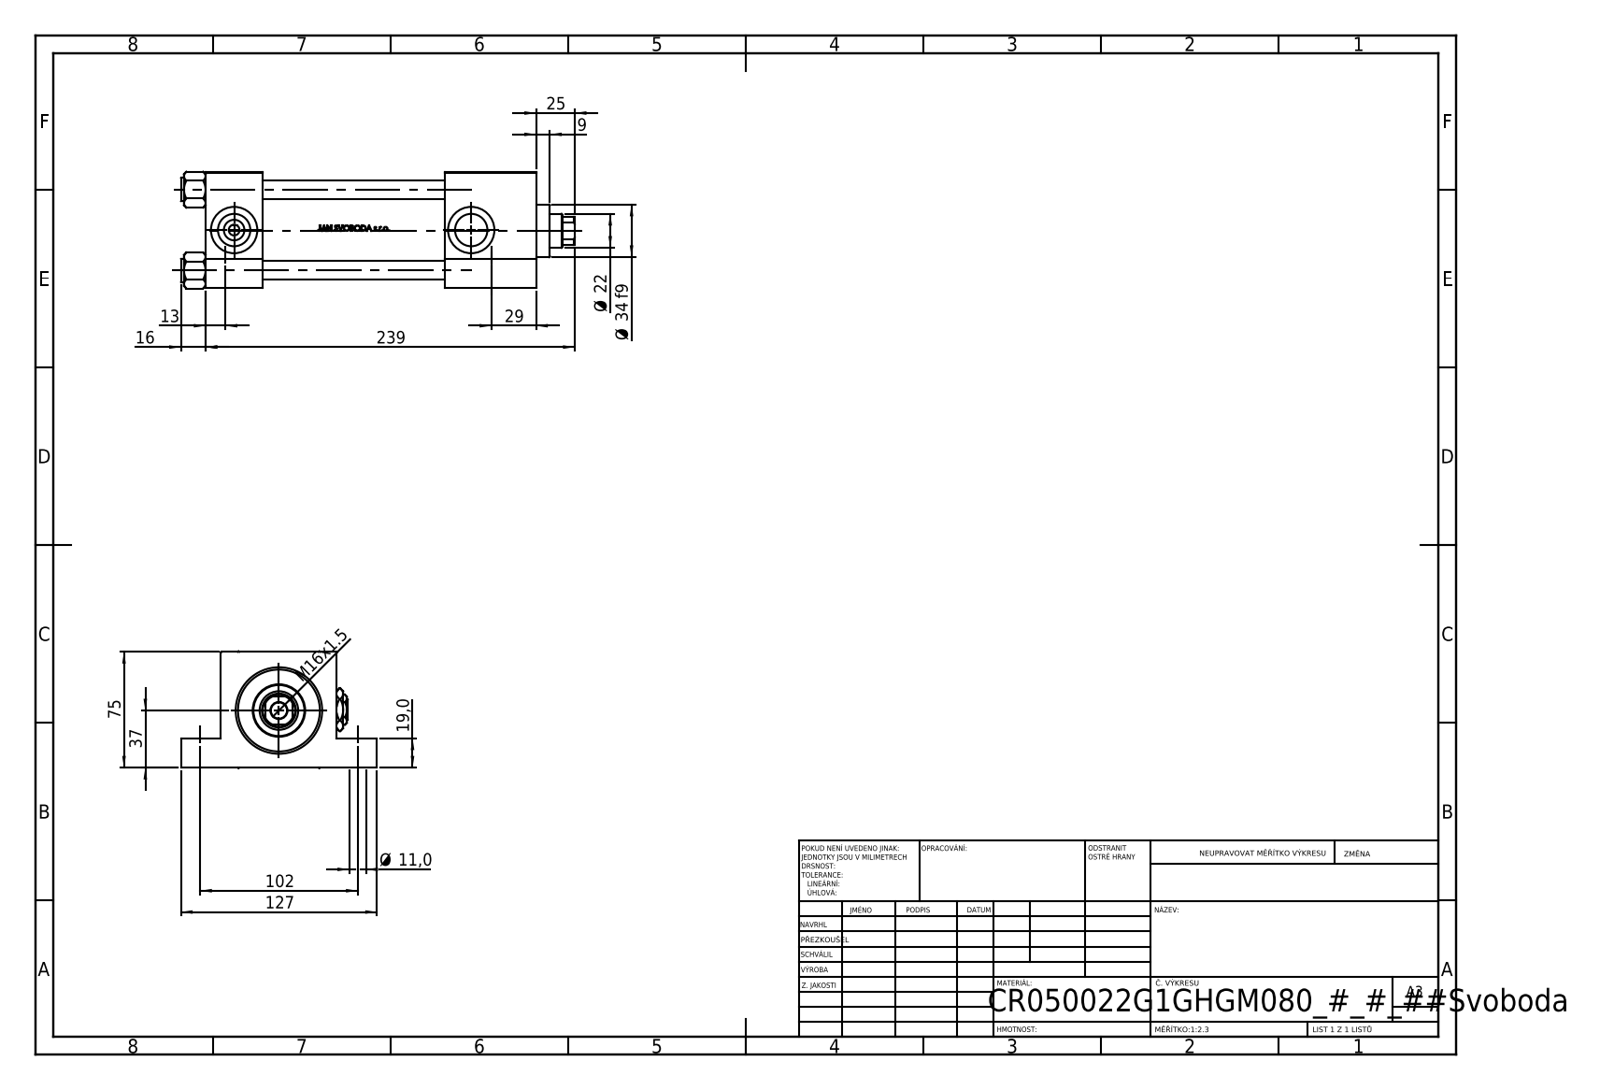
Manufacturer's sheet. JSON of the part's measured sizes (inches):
{"part_name": "Zatka_pro_OIL_PORT; V215CR_VCP_G; V215CR_G_Body; NUT_M5_G (+2 more)", "step_written_by": "SolidWorks 2019 (CONFIG_CONTROL_DESIGN)", "units": "inches", "bodies": {"solids": 12, "faces": 1134, "planar": 454, "cylindrical": 128, "other": 552}, "overall_size": [10.039, 5, 2.974], "volume_in3": 50.79, "surface_area_in2": 301.4, "round_holes": [[0.433, 4], [0.472, 4], [0.276, 2], [0.825, 2], [1.181, 2], [0.413, 1], [0.866, 1], [0.984, 1], [1.614, 1], [1.969, 1], [2.087, 1]], "round_bosses_or_shafts": [[0.591, 4], [2.205, 1], [1.339, 1]], "partial_cylinders_radius": [[0.413, 1]], "face_to_face_distances": [2.953, 1.457, 8.425, 6.969, 0.748, 2.205, 6.102, 4.646, 2.323, 1.024], "hole_center_spacings": [2.059, 1.442, 1.47, 2.912, 4.016, 6.772, 7.873, 6.043]}
